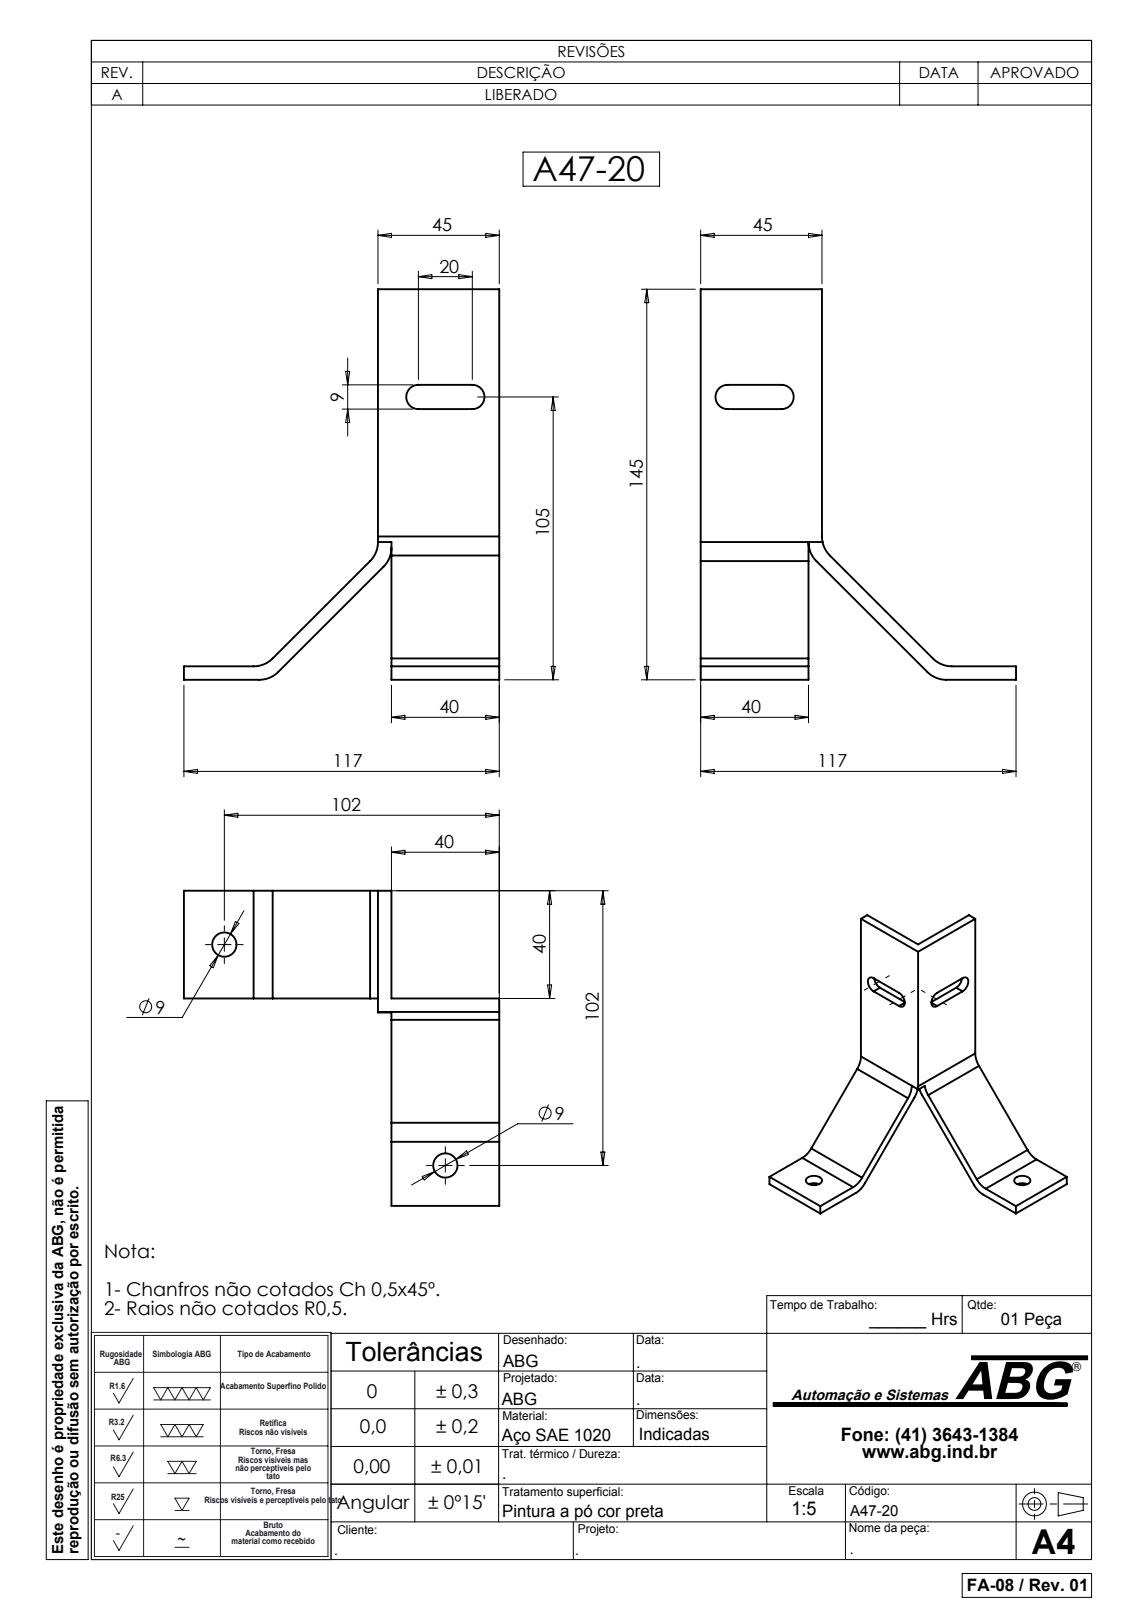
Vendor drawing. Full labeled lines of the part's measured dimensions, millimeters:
Part name (STEP PRODUCT): A47-20
STEP written by: SolidWorks 2007 (CONFIG_CONTROL_DESIGN)
Units: millimetres
Bodies: 1 solid, 41 faces (24 planar, 17 cylindrical, 0 other)
Overall size (bounding box): 145 × 117 × 117
Volume: 75 648 mm³ · Surface area: 34 818 mm²
Round holes (diameter × count): ⌀9 ×2
Partial cylindrical surfaces — rounded edges, fillets, slot ends (radius × count): R10 ×8, R4.5 ×4
Main face-to-face distances: 5, 40, 45, 145, 140, 117, 77, 72, 100.5, 95.5
Hole centre spacings: 115.97
